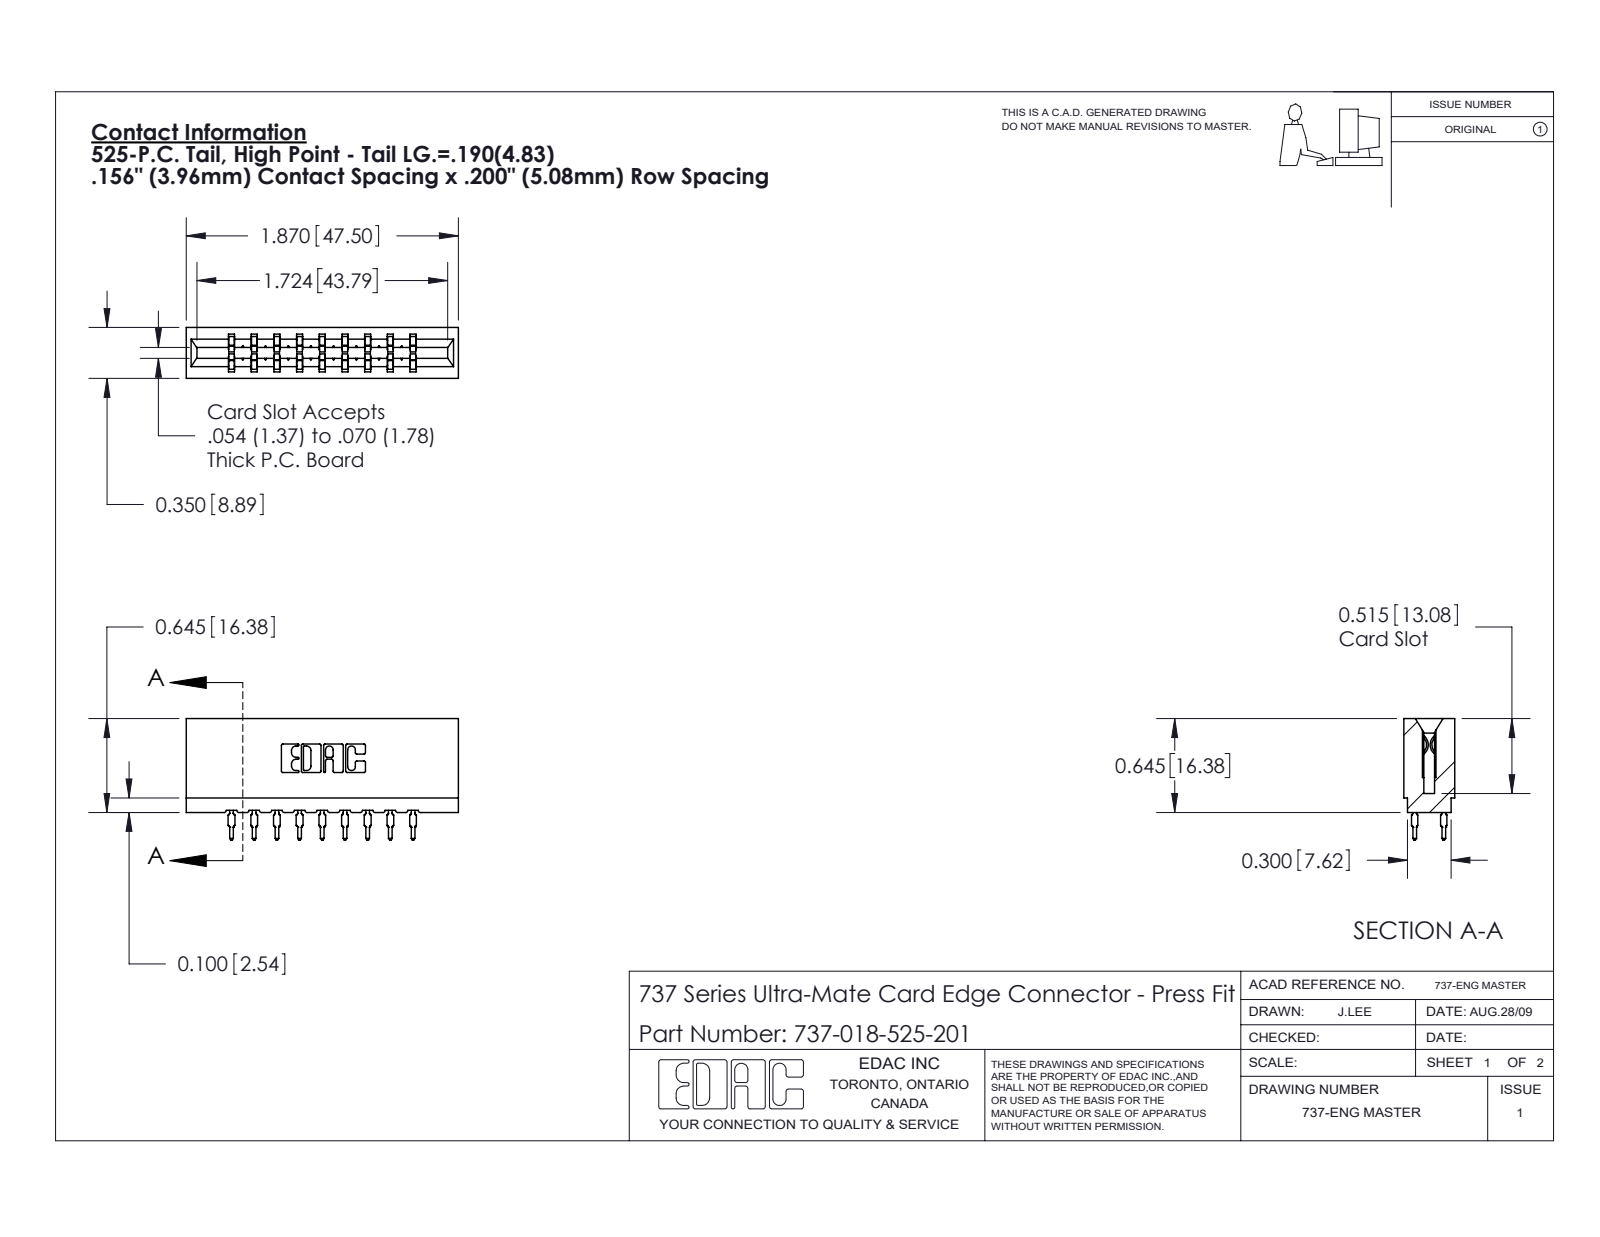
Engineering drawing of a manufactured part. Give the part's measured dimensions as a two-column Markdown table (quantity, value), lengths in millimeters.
| quantity | value |
| --- | --- |
| part name | 737-018-525-201; 737 Part_Insulator Option - 01; 745-292-001_525 |
| STEP written by | SolidWorks 2020 (CONFIG_CONTROL_DESIGN) |
| units | millimeters |
| bodies | 19 solids, 1714 faces (891 planar, 355 cylindrical, 468 other) |
| overall size | 47.5 × 21.2 × 8.9 |
| volume | 4 900 mm³ |
| surface area | 6 363 mm² |
| partial cylindrical surfaces (radius × count) | 0.5 × 36, 0.3 × 22, 0.4 × 18, 0.1 × 8, 0.3 × 8, 0.2 × 6, 0.8 × 6, 0.7 × 3 |
| main face-to-face distances | 4, 3.5, 5.4, 15.8, 8.9, 7.9, 11.9, 9, 19.8, 5 |
